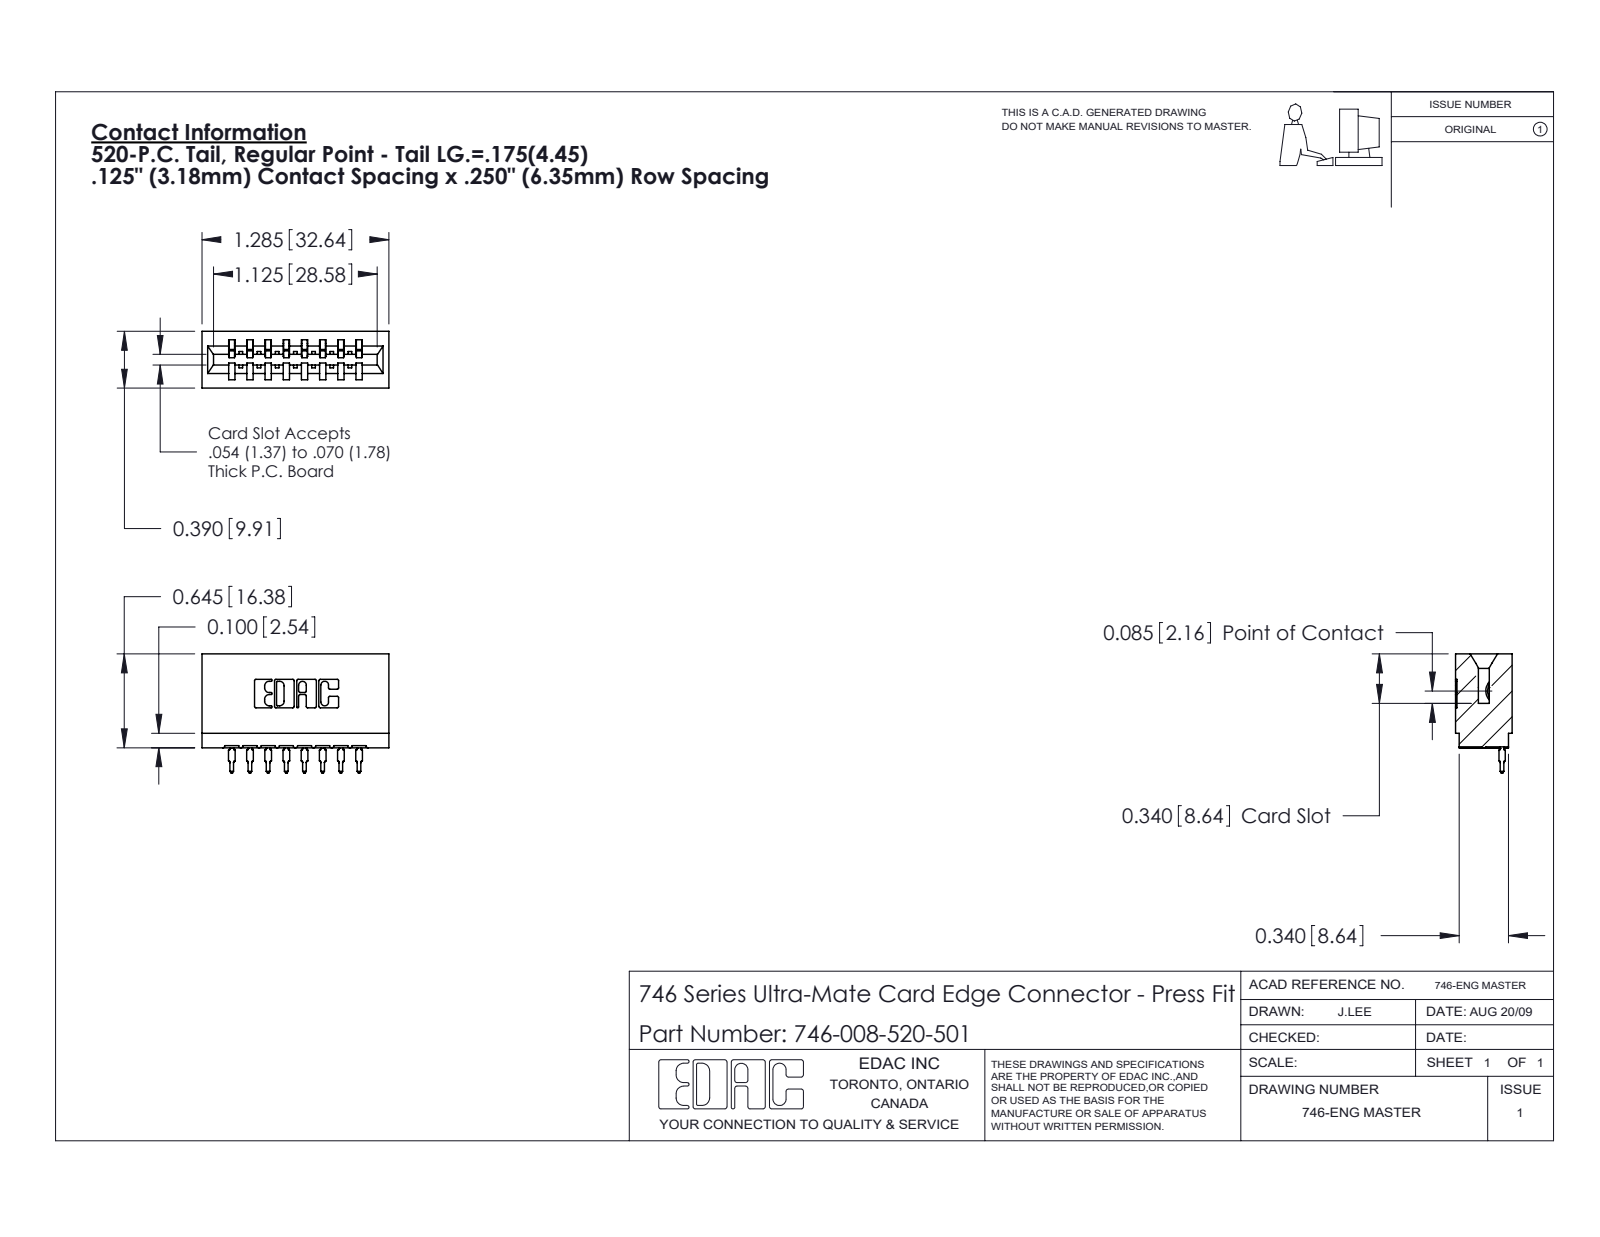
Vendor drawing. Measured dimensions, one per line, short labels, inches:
name: 746 Part_.340 Slot Depth - 01; 746-292-001_520; 746-008-520-501
written by: SolidWorks 2020 (CONFIG_CONTROL_DESIGN)
unit: in
bodies: 9 solids, 961 faces (559 planar, 194 cylindrical, 208 other)
size: 1.285 × 0.819 × 0.39
volume: 0.236 in³; area: 7.173 in²
rounds: 22× R0.01, 16× R0.021, 9× R0.015, 6× R0.007, 6× R0.031, 4× R0.005, 4× R0.011, 3× R0.026
face distances: 0.25, 0.042, 0.125, 0.5, 0.333, 0.292, 0.375, 0.208, 0.125, 0.057
